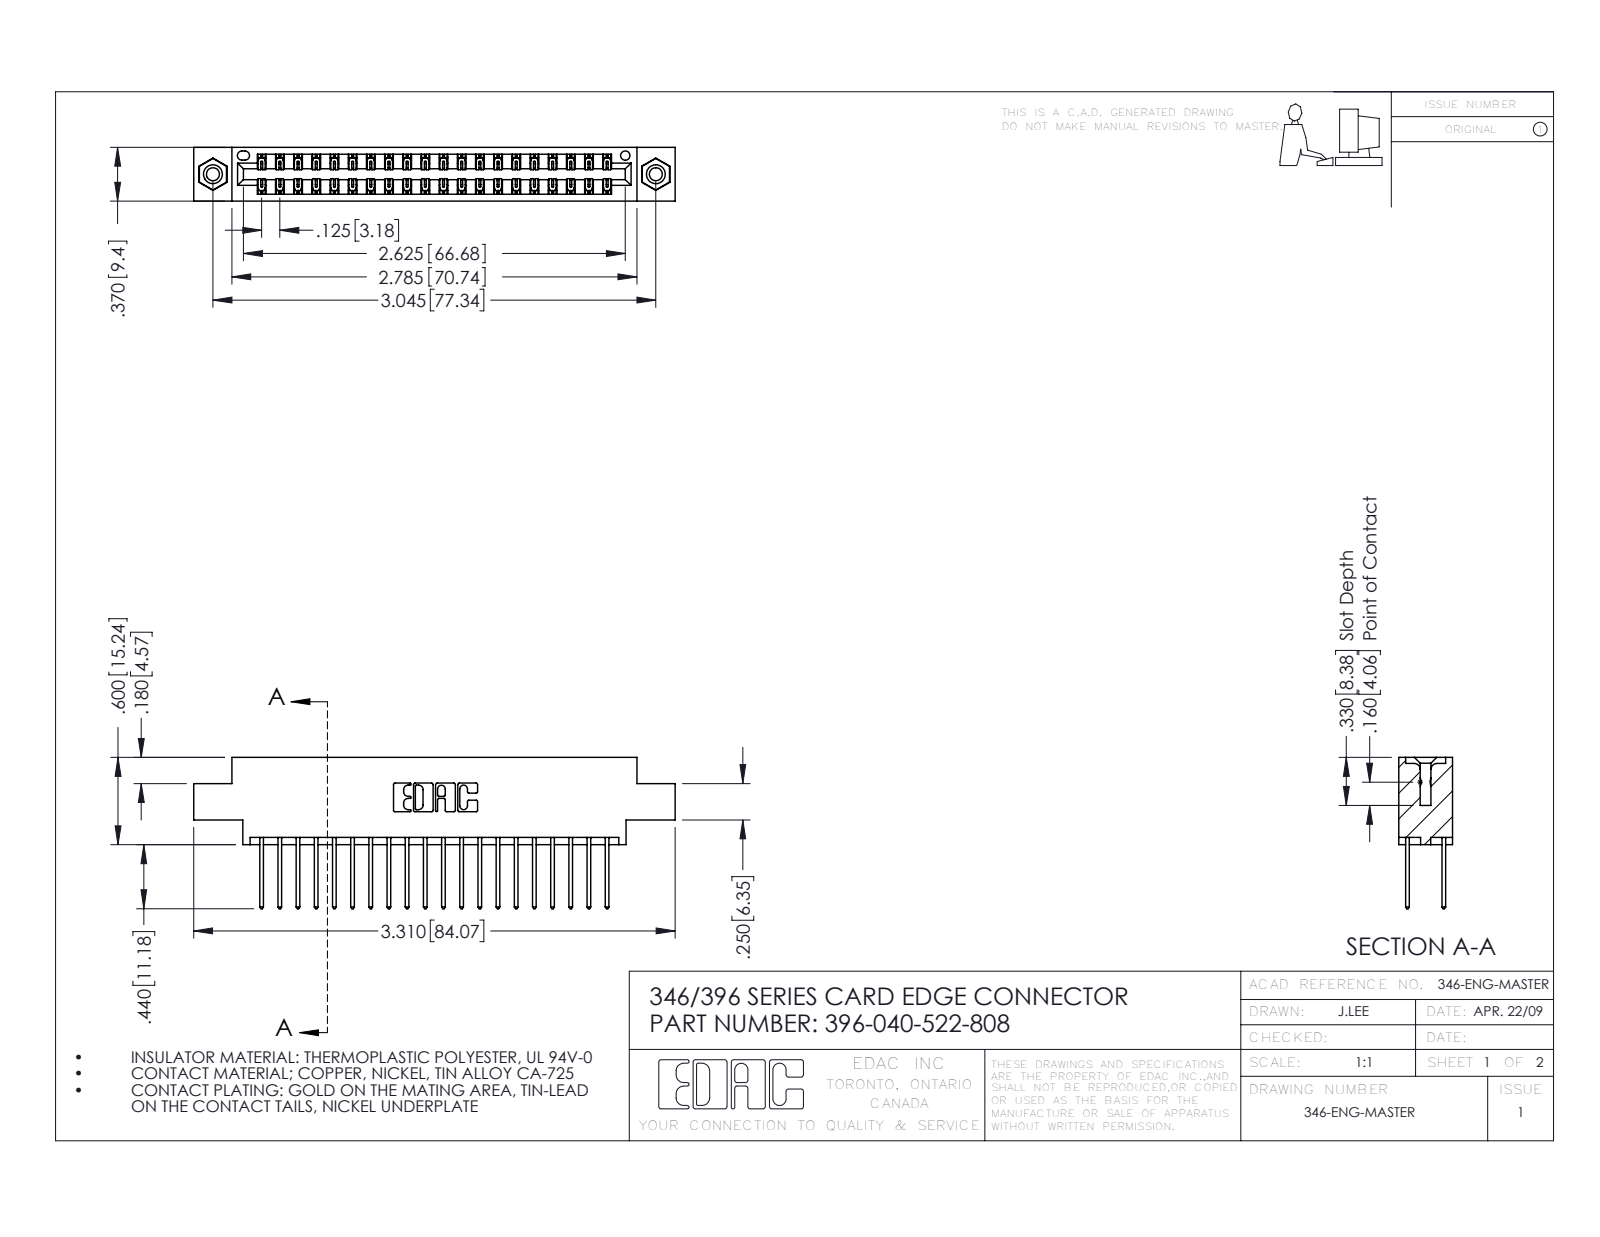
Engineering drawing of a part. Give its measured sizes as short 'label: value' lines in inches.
name: 346 Part_0.170 Offset - 0.156 Dia-TI; 345-292-001_345-293-122; 345-250-001_345-250-003-102; 396-040-522-808
written by: SolidWorks 2016 (CONFIG_CONTROL_DESIGN)
unit: in
bodies: 43 solids, 2266 faces (1512 planar, 738 cylindrical, 16 other)
size: 3.31 × 1.04 × 0.37
volume: 0.486 in³; area: 17.49 in²
holes: 2× ⌀0.089, 2× ⌀0.125, 2× ⌀0.156, 1× ⌀0.064
bosses: 2× ⌀0.155
rounds: 60× R0.006, 40× R0.01, 22× R0.01, 6× R0.007, 6× R0.031, 3× R0.026, 2× R0.014, 2× R0.022
face distances: 0.048, 0.322, 0.25, 0.37, 0.072, 0.298, 0.025, 0.275, 0.222, 0.148
hole spacings: 0.246, 2.837, 3.045
